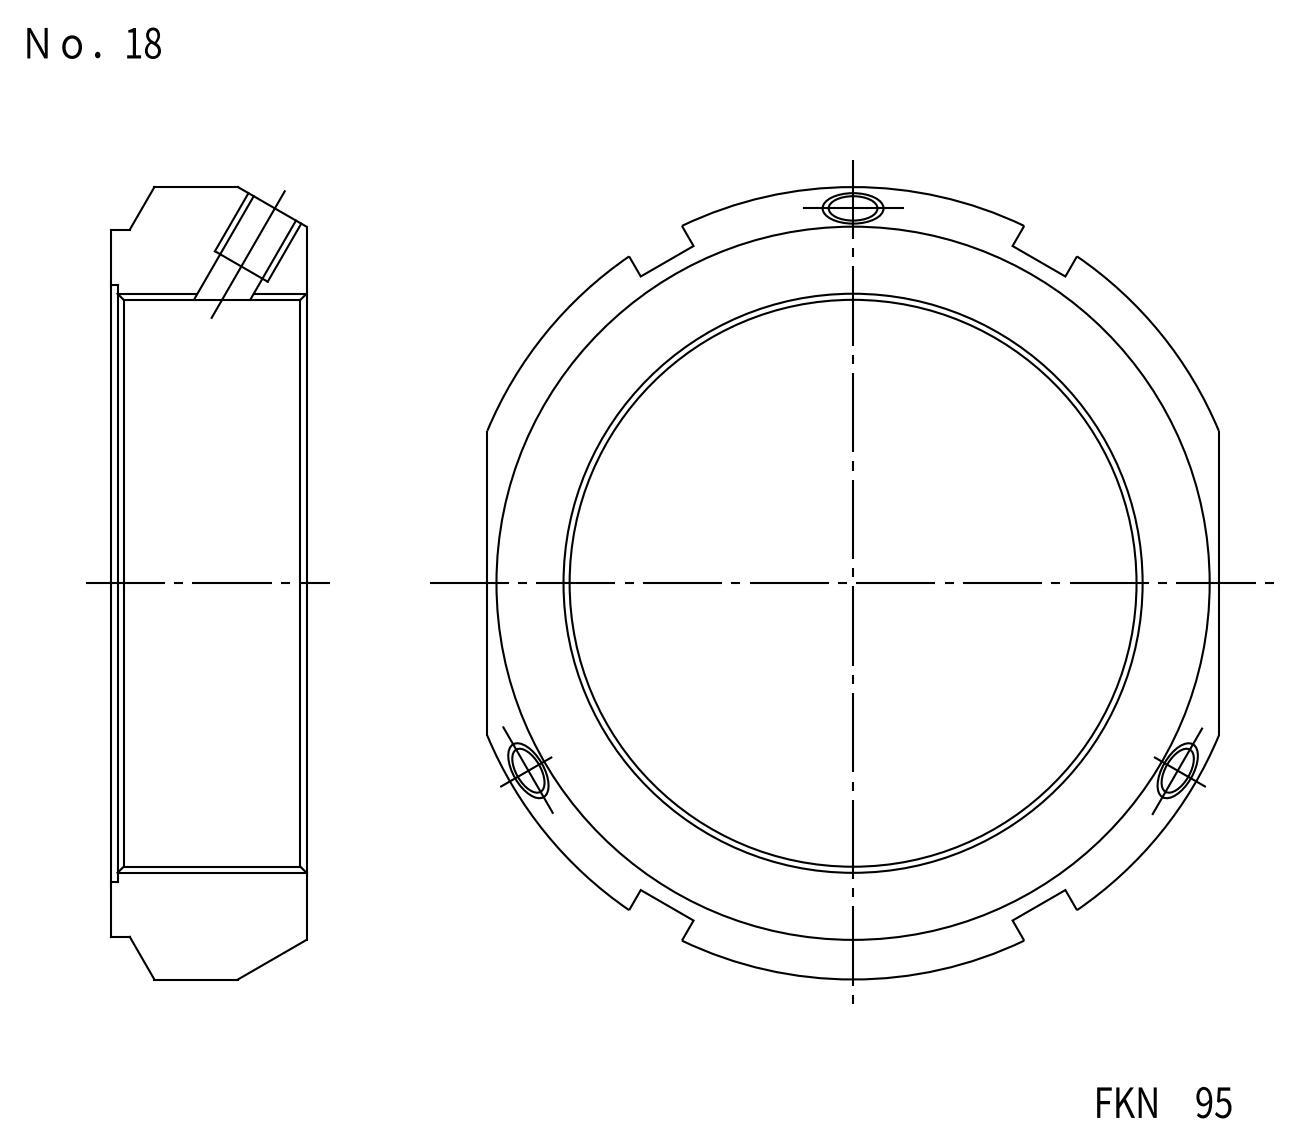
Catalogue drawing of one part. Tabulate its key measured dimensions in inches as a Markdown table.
| quantity | value |
| --- | --- |
| part name | FKD FKN95 |
| STEP written by | Autodesk Inventor LT (CONFIG_CONTROL_DESIGN) |
| units | inches |
| bodies | 1 solid, 37 faces (20 planar, 15 cylindrical, 2 other) |
| overall size | 5.118 × 4.724 × 1.26 |
| volume | 9.606 in³ |
| surface area | 50.49 in² |
| round holes (diameter × count) | 0.33 × 3, 0.402 × 3, 3.74 × 1, 3.858 × 1 |
| round bosses / shafts (diameter × count) | 4.567 × 1 |
| partial cylindrical surfaces (radius × count) | 2.559 × 1 |
| main face-to-face distances | 1.26, 4.724, 4.803, 0.059, 1.201, 0.394 |
